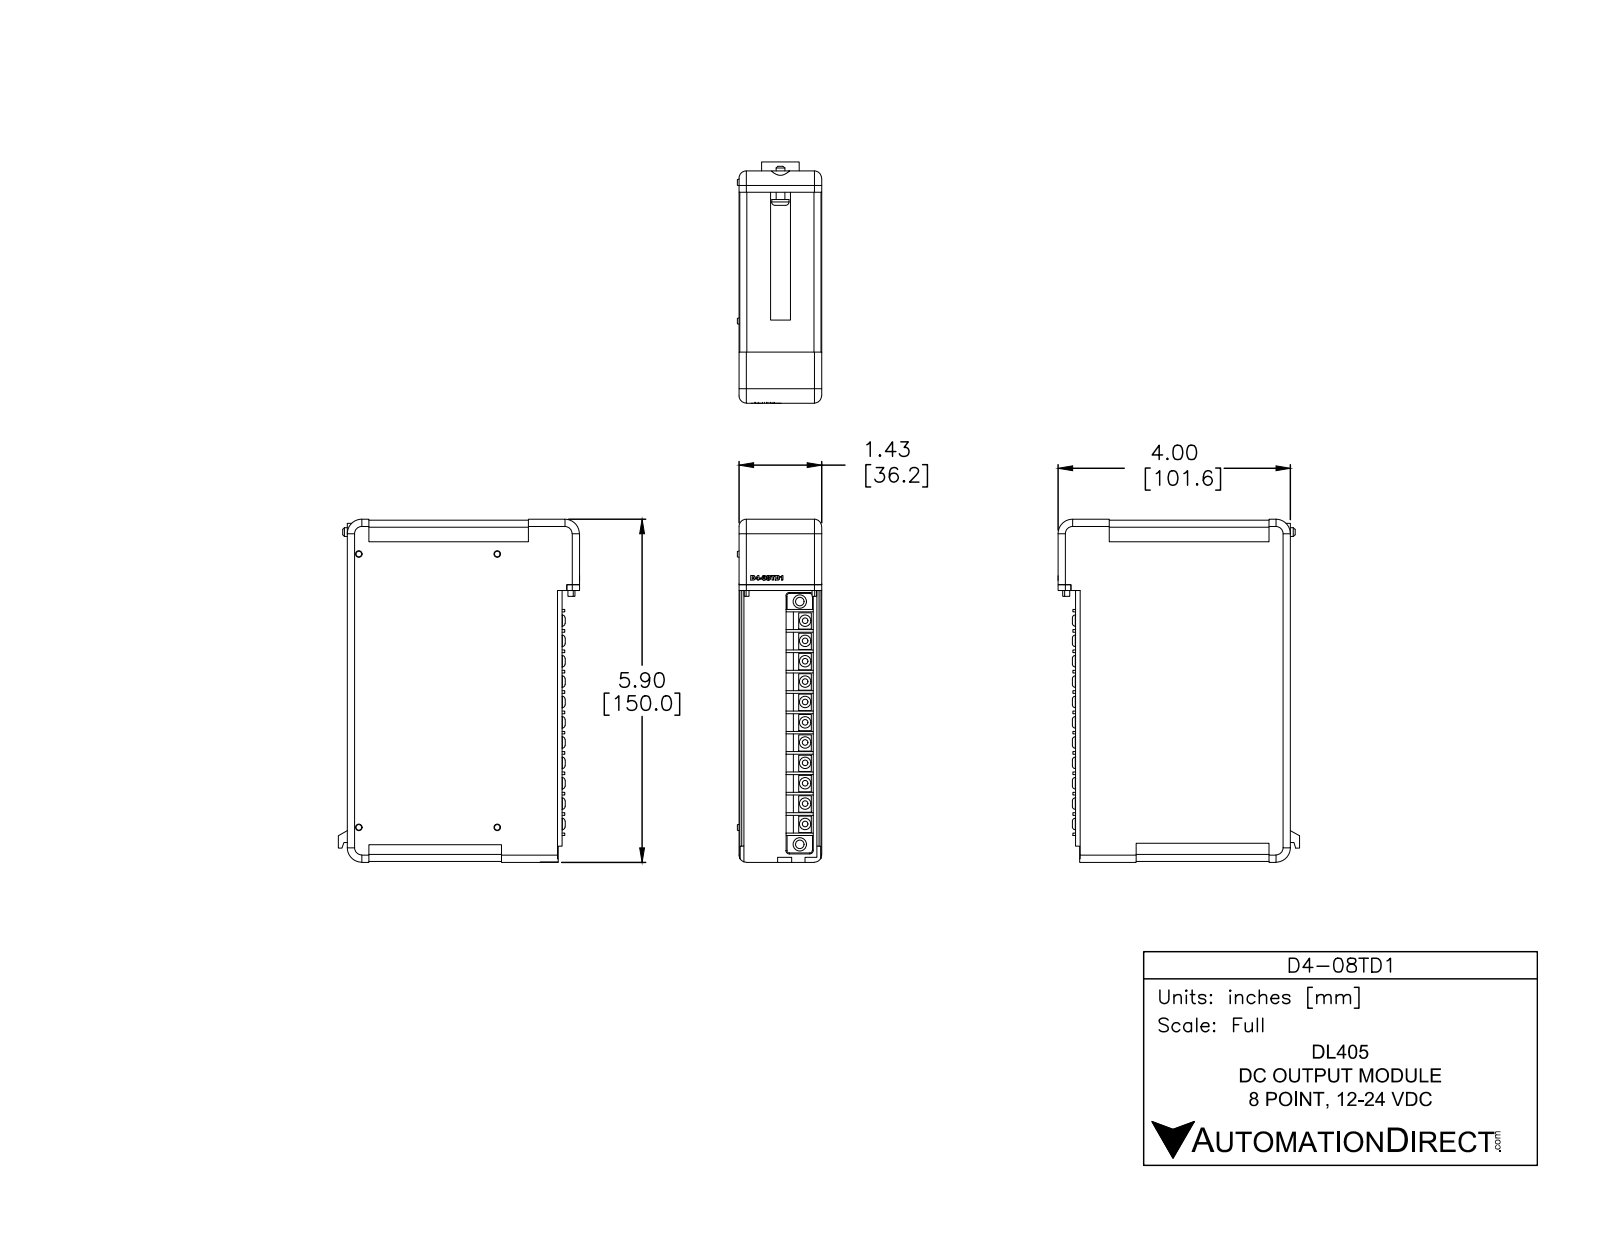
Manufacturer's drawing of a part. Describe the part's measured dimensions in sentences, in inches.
The part is named "D4-08TD1". Its 3-D file was written by "SolidWorks 2014 (AUTOMOTIVE_DESIGN)". It is 11 solids with 449 faces: 293 planar, 71 cylindrical and 85 other. Overall it measures 5.905 by 4.156 by 1.455 inches. Its volume is 29.11 cubic inches and its surface area 85.82 square inches. Round bosses or shafts: 11 of diameter 0.2, 2 of diameter 0.229, 1 of diameter 0.3, 1 of diameter 0.15. Partial cylindrical surfaces (rounded edges, fillets, slot ends): 8 of radius 0.125, 6 of radius 0.015, 4 of radius 0.06, 4 of radius 0.12, 3 of radius 0.25, 2 of radius 0.03, 1 of radius 0.151, 1 of radius 0.171. The main face-to-face distances are 1.425, 0.015, 3.325, 0.085, 1.34, 5.875, 0.07, 0.2, 1.41, 1.325.
